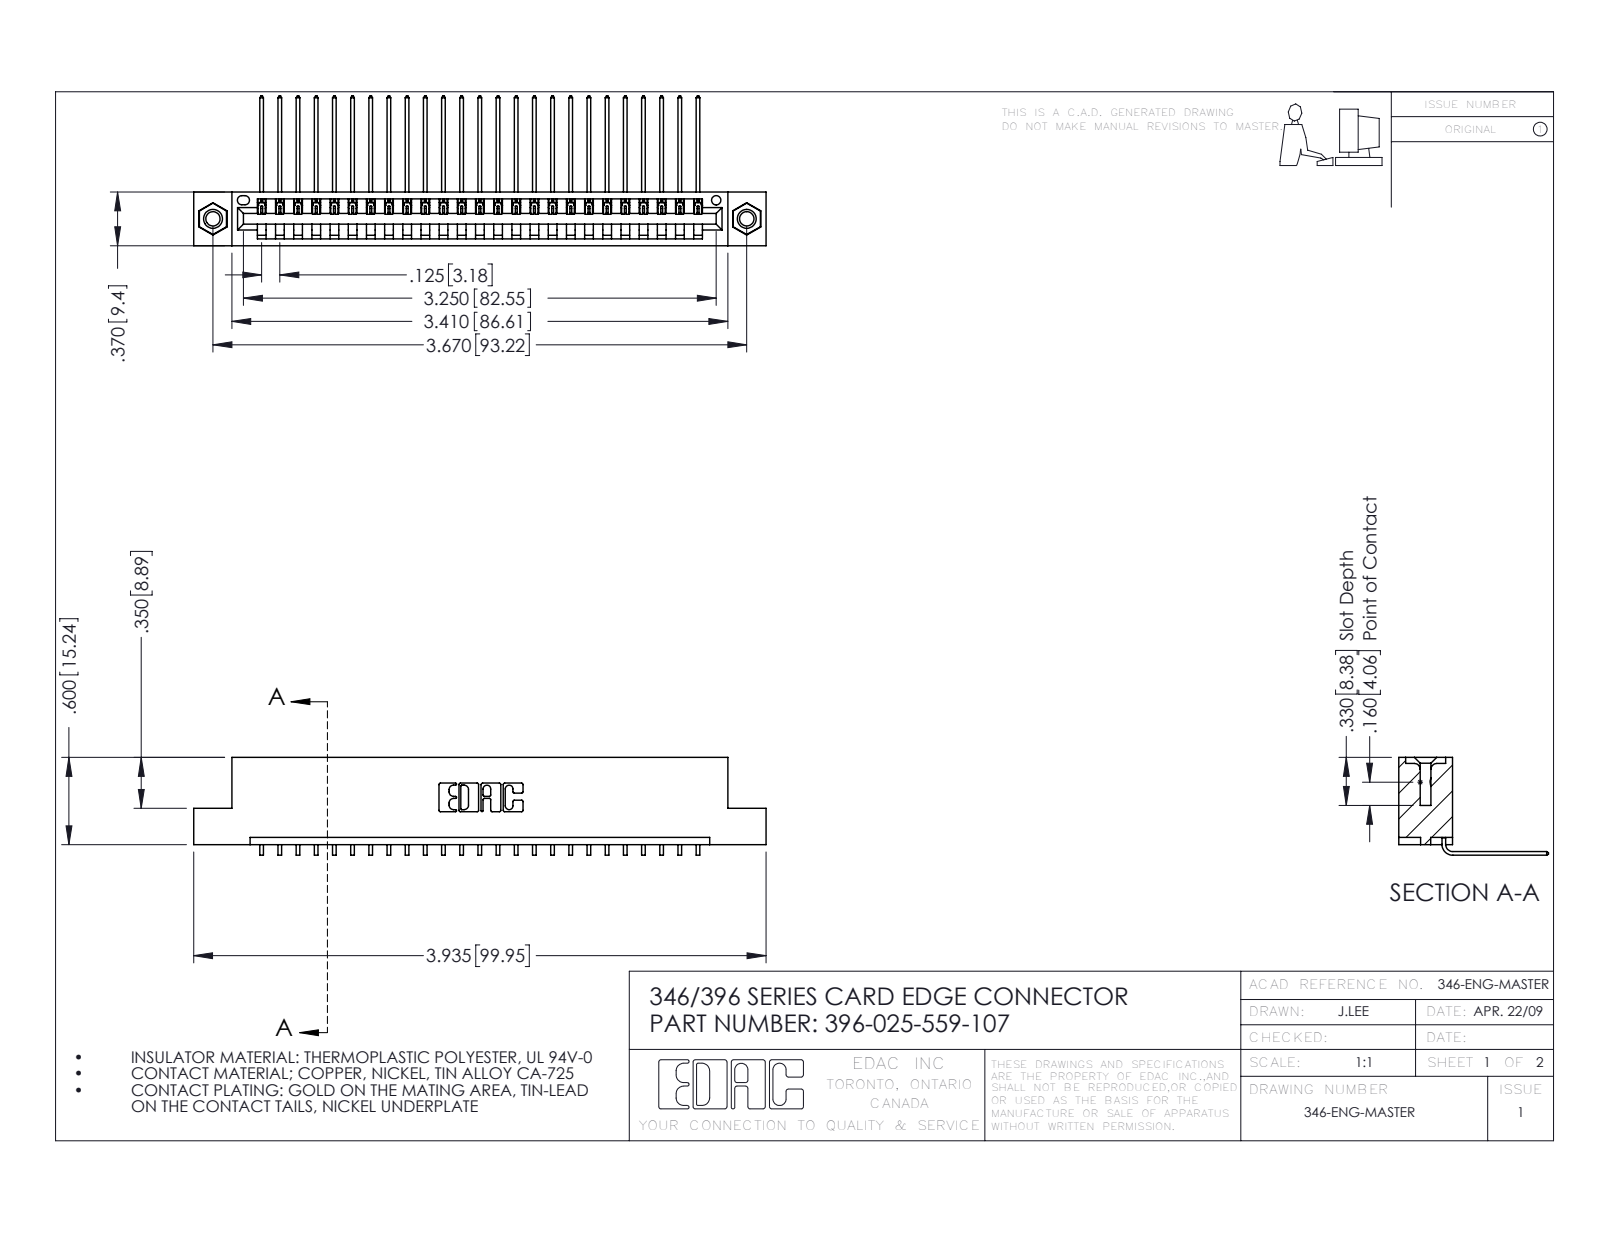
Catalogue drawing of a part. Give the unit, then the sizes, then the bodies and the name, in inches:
Units: inches
Overall size (bounding box): 3.935 × 1.03 × 0.673
Round holes (diameter × count): ⌀0.098 ×2, ⌀0.125 ×2, ⌀0.156 ×2, ⌀0.064 ×1
Round bosses / shafts (diameter × count): ⌀0.155 ×2
Partial cylindrical surfaces — rounded edges, fillets, slot ends (radius × count): R0.006 ×50, R0.01 ×22, R0.007 ×6, R0.031 ×6, R0.026 ×3, R0.031 ×2, R0.04 ×2, R0.014 ×1
Main face-to-face distances: 0.048, 0.322, 0.37, 0.25, 0.072, 0.025, 0.298, 0.148, 0.222, 0.1
Hole centre spacings: 0.246, 3.462, 3.67
Volume: 0.581 in³ · Surface area: 18.98 in²
Bodies: 28 solids, 1682 faces (1158 planar, 508 cylindrical, 16 other)
Part name (STEP PRODUCT): 345-292-001_558 559 Tail - 1; 396-025-559-107; 346 Part_Flush Mounting Lugs - 0.156 Dia-TI; 345-250-001_345-250-005-103
STEP written by: SolidWorks 2016 (CONFIG_CONTROL_DESIGN)
